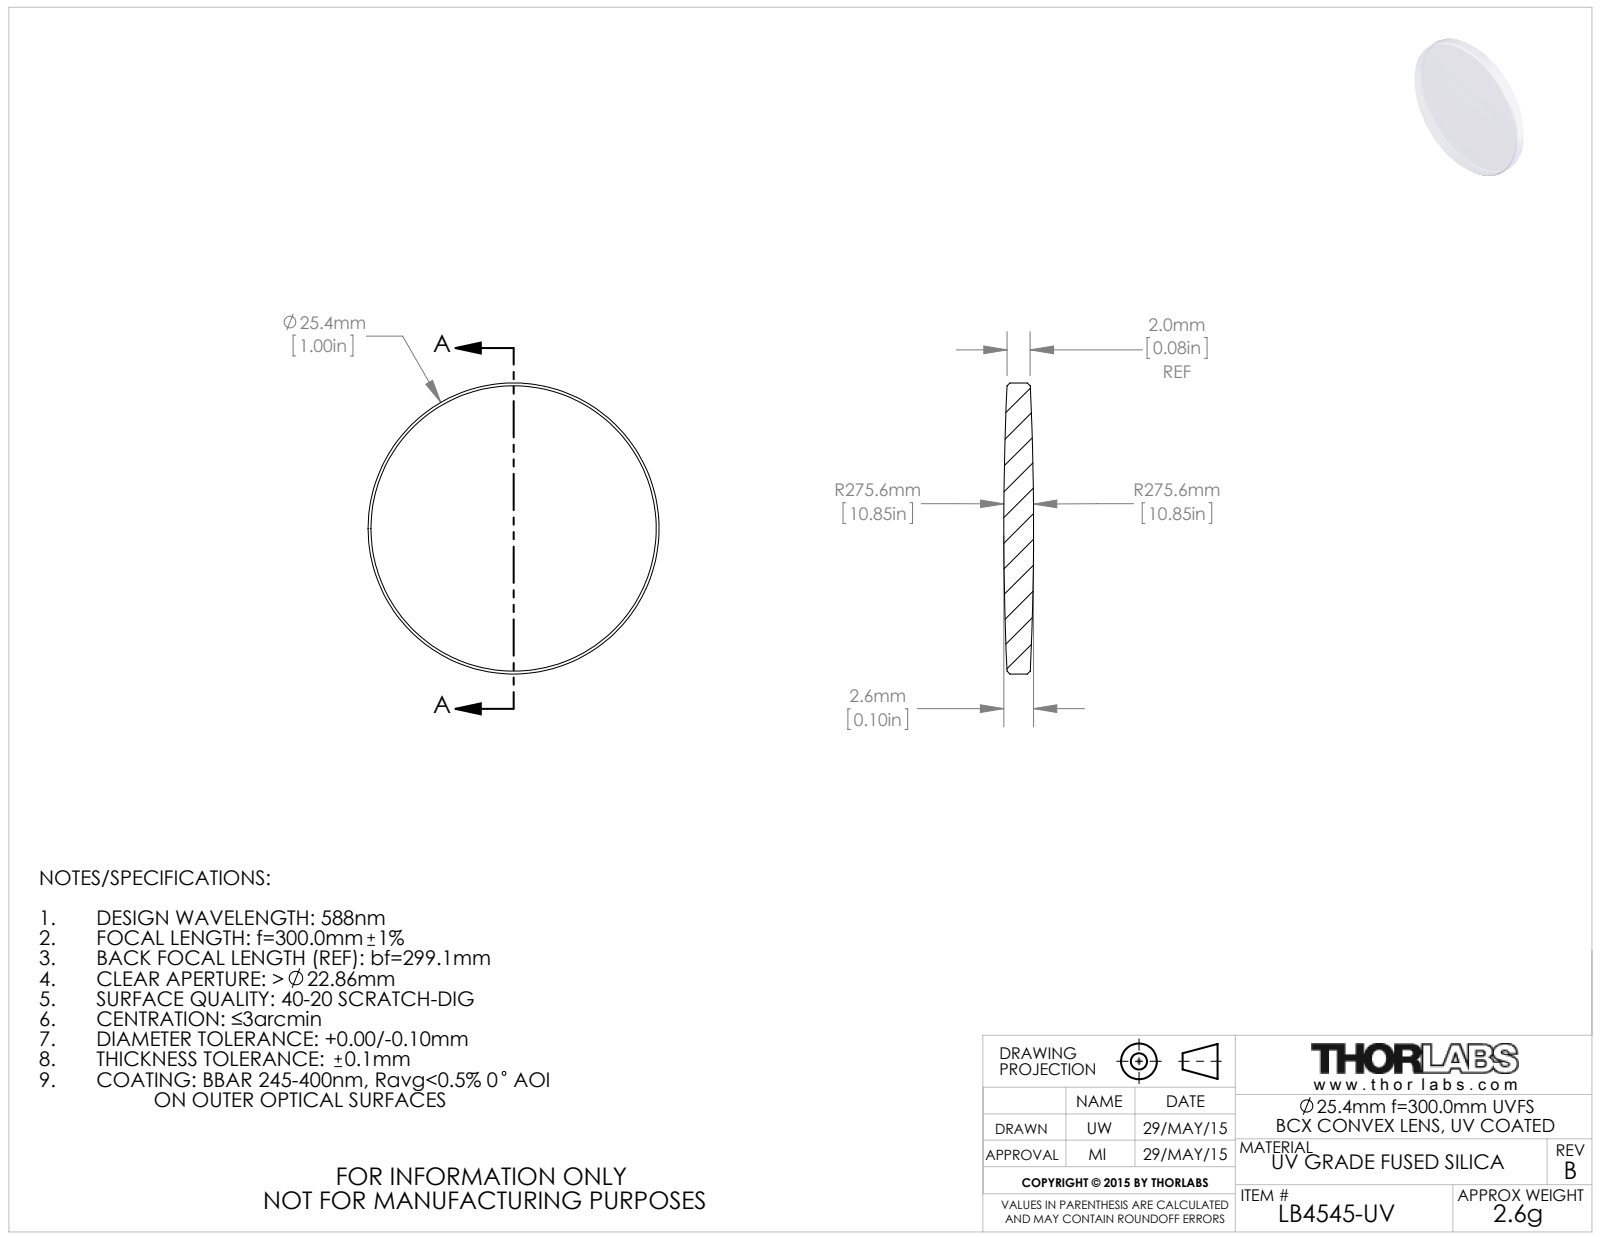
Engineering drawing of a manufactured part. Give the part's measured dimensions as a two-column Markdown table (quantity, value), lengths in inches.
| quantity | value |
| --- | --- |
| part name | 4327-E0W |
| STEP written by | SolidWorks 2014 (CONFIG_CONTROL_DESIGN) |
| units | inches |
| bodies | 1 solid, 10 faces (0 planar, 2 cylindrical, 8 other) |
| overall size | 1 × 1 × 0.102 |
| volume | 0.071 in³ |
| surface area | 1.786 in² |
| round bosses / shafts (diameter × count) | 1 × 1 |
